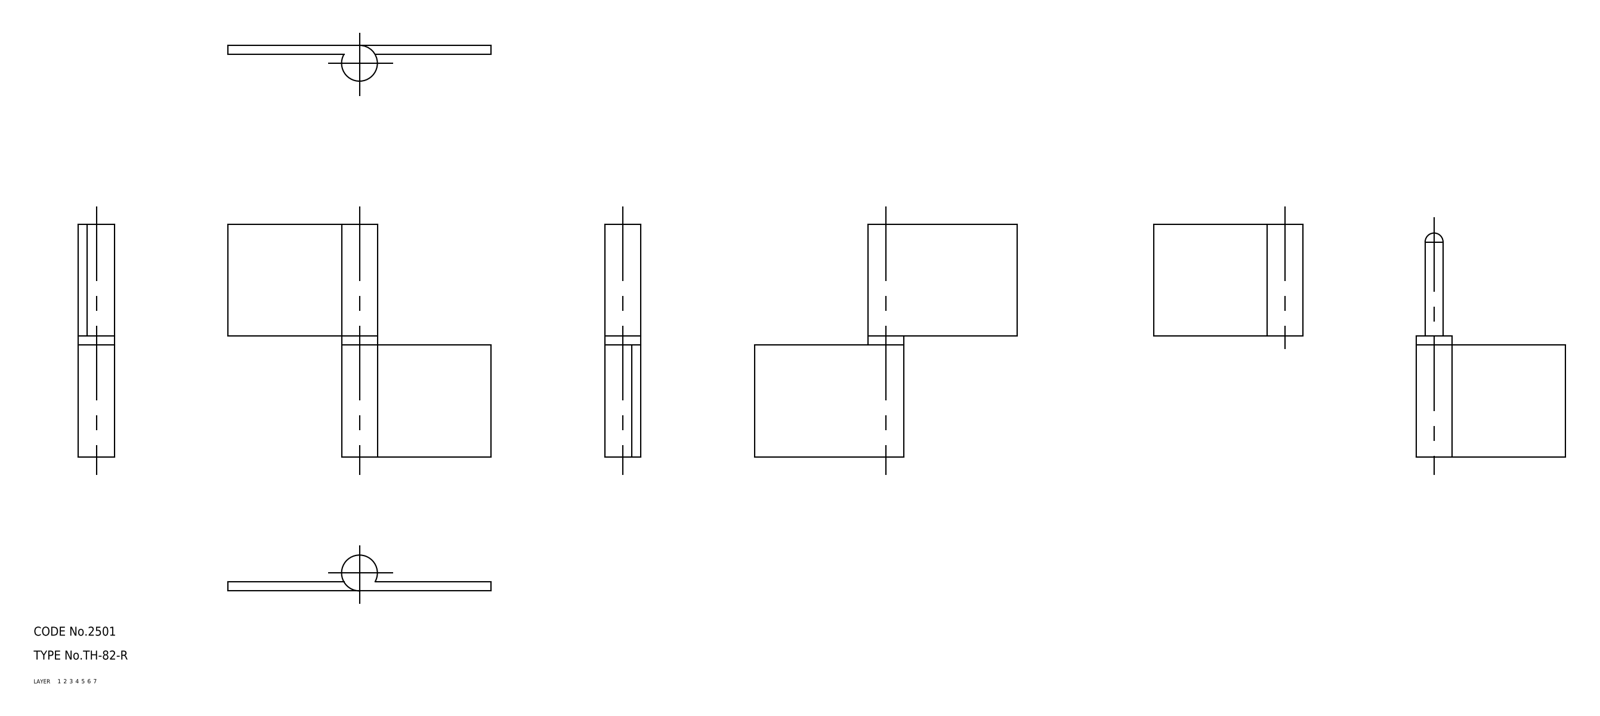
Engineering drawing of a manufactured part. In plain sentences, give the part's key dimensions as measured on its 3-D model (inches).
The part is named "washer; shaft; hinge piece_B; hinge piece_A (+1 more)". Its 3-D file was written by "CADfix (AUTOMOTIVE_DESIGN)". It is 4 solids with 28 faces: 0 planar, 0 cylindrical and 28 other. Overall it measures 3.465 by 3.071 by 0.472 inches. Its volume is 1.077 cubic inches and its surface area 20.3 square inches.
